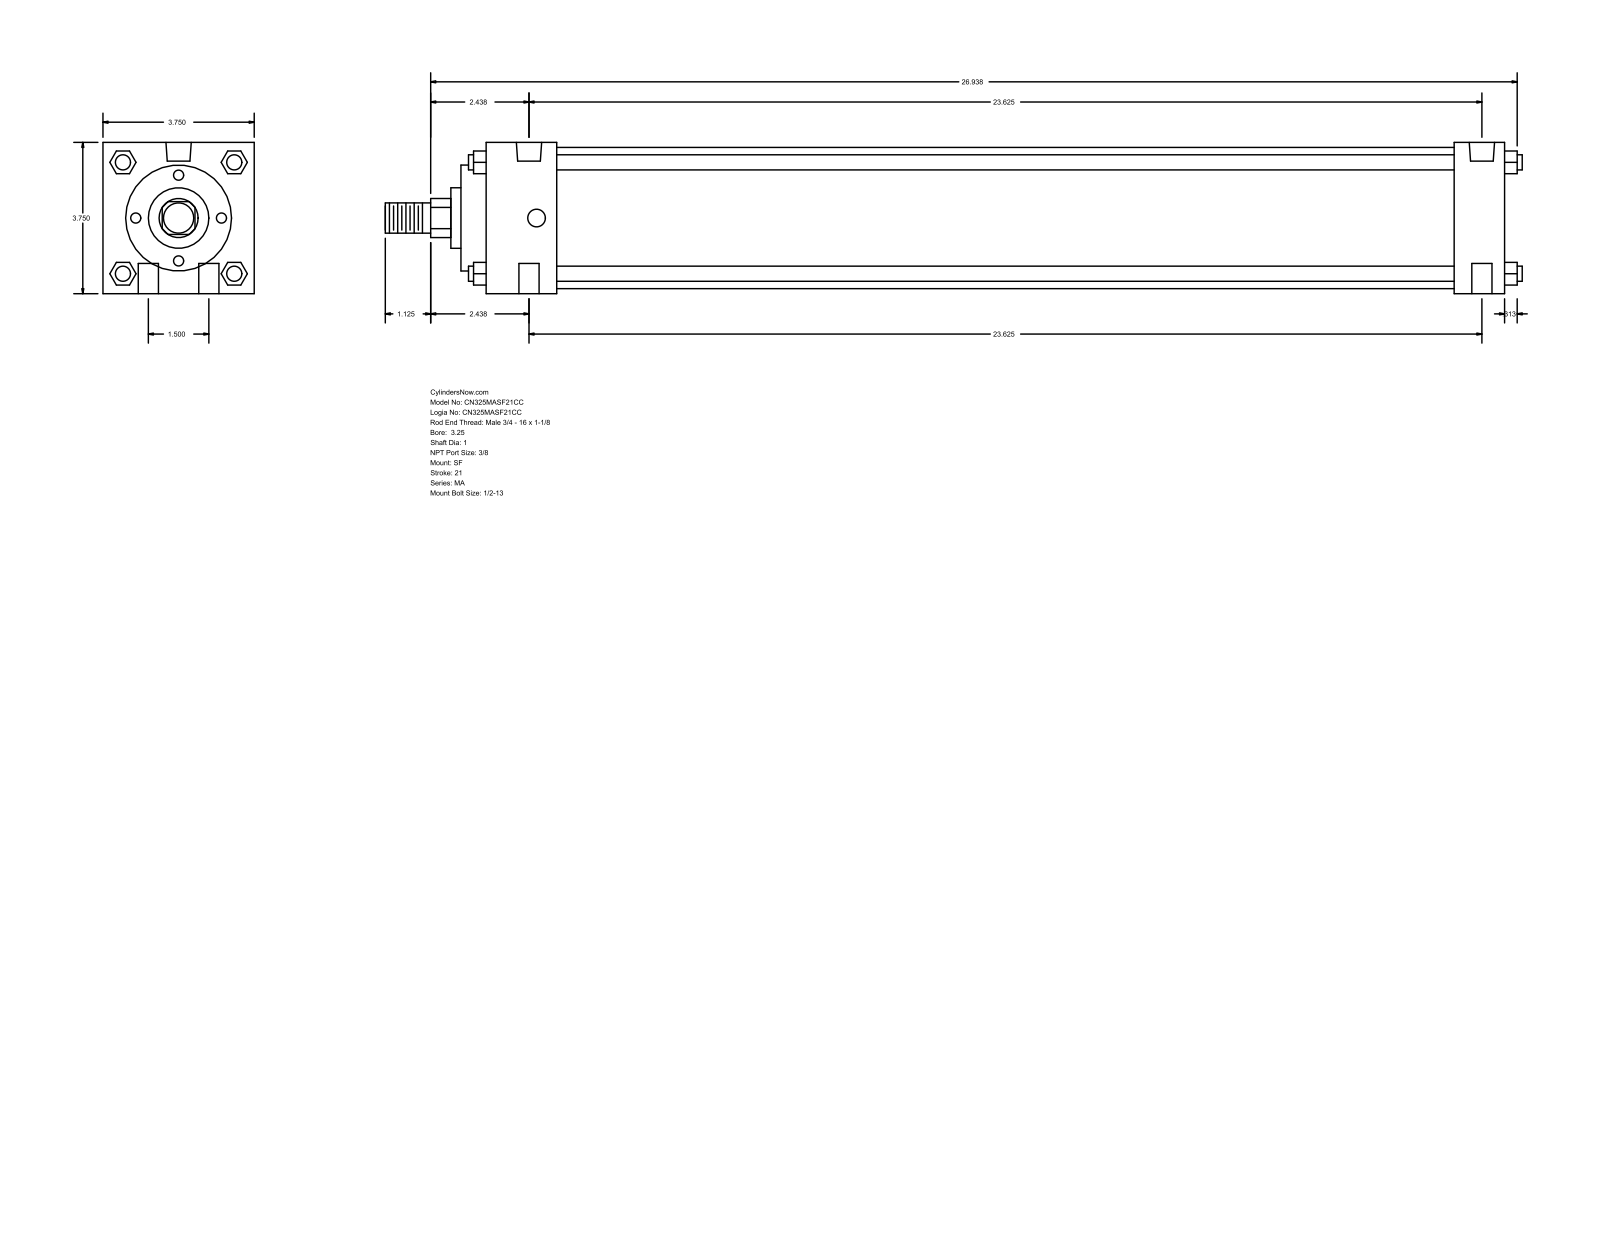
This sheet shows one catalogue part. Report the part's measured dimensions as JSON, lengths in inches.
{"part_name": "MA_SF__0325_1", "step_written_by": "GSSL Pune (CONFIG_CONTROL_DESIGN)", "units": "inches", "bodies": {"solids": 0, "faces": 126, "planar": 95, "cylindrical": 31, "other": 0}, "overall_size": [28.187, 3.75, 3.75], "round_holes": [[0.5, 4], [0.437, 2], [0.627, 2]], "round_bosses_or_shafts": [[0.375, 4], [3.5, 1], [2.625, 1], [1.5, 1], [1, 1], [0.75, 1]], "partial_cylinders_radius": [[0.484, 1]], "face_to_face_distances": [3.75, 25.25, 25.875, 24, 1.25, 1.75, 22.25, 23.5, 0.625, 2.375], "hole_center_spacings": [0.75, 23.637, 23.625, 1.5, 23.673, 23.25]}
